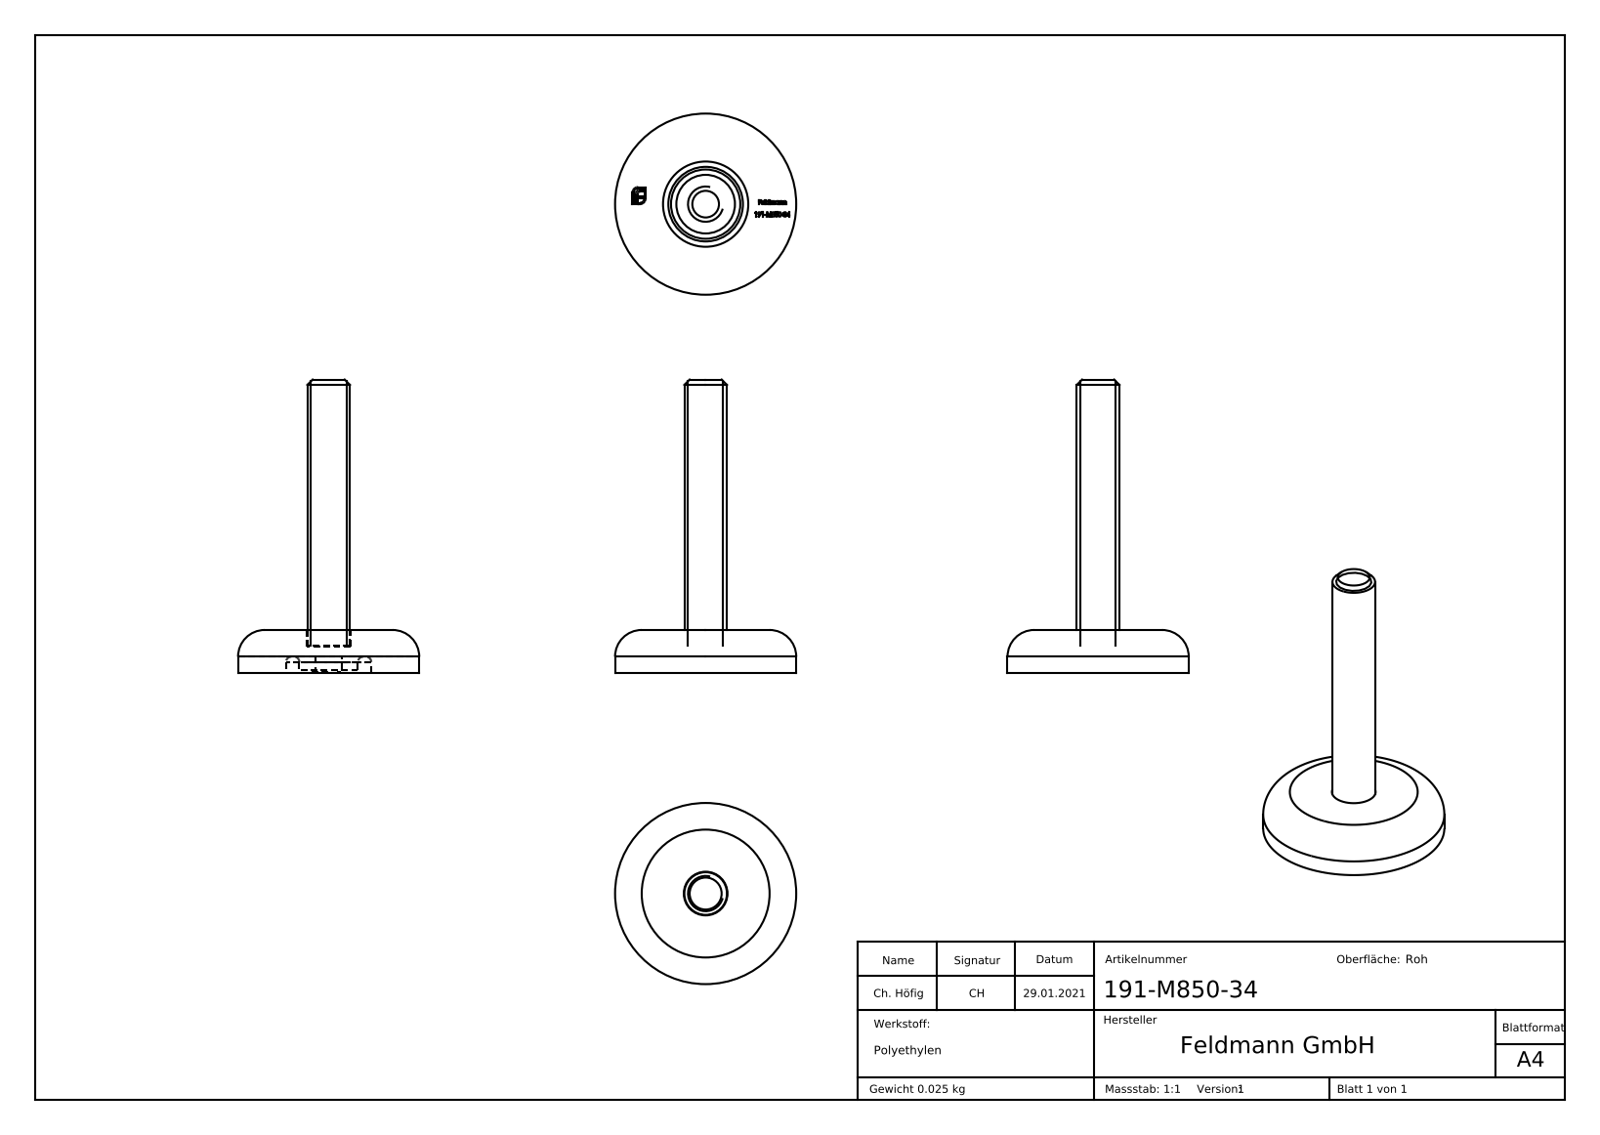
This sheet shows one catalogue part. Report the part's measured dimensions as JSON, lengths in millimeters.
{"part_name": "191-M850-34", "step_written_by": "SolidWorks 2018 (CONFIG_CONTROL_DESIGN)", "units": "millimeters", "bodies": {"solids": 2, "faces": 313, "planar": 168, "cylindrical": 12, "other": 133}, "overall_size": [55, 34, 34], "volume_mm3": 8669, "surface_area_mm2": 4100, "round_holes": [[5, 1], [8.2, 1], [16, 1]], "round_bosses_or_shafts": [[34, 1], [11, 1], [8, 1]], "face_to_face_distances": [8, 5, 3, 0.5, 7.5, 4.9, 3.1, 4.4, 4.5, 1.9]}
